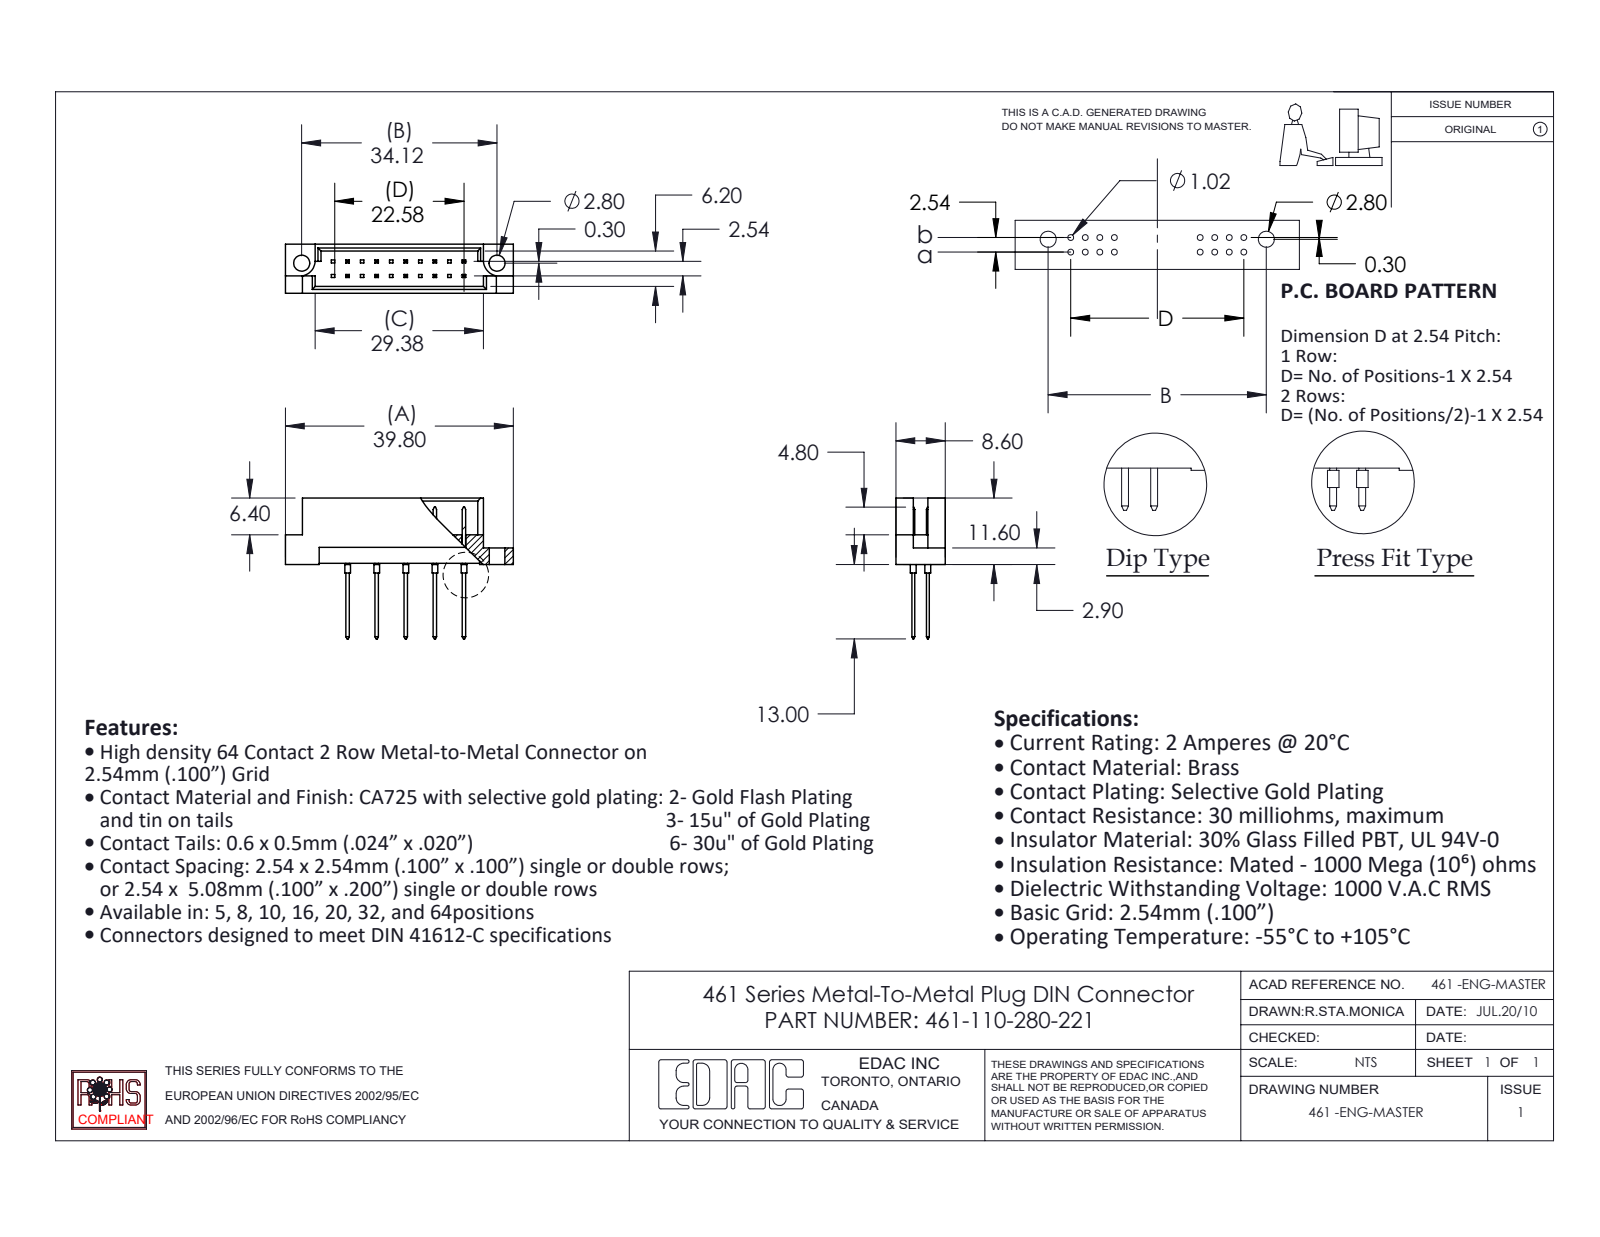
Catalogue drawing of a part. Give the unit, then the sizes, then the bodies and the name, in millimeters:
Units: millimetres
Overall size (bounding box): 39.8 × 24.6 × 8.6
Round holes (diameter × count): ⌀2.8 ×2
Round bosses / shafts (diameter × count): ⌀1 ×10
Partial cylindrical surfaces — rounded edges, fillets, slot ends (radius × count): R2.8 ×2
Main face-to-face distances: 1.2, 7.4, 8.6, 6.2, 5.08, 2.54, 2.78, 3.28, 5.32, 5.82
Hole centre spacings: 34.12
Volume: 1 980 mm³ · Surface area: 2 864 mm²
Bodies: 11 solids, 348 faces (322 planar, 26 cylindrical, 0 other)
Part name (STEP PRODUCT): 461 Part_20; 461-290_80; 461-110-280-221
STEP written by: SolidWorks 2020 (CONFIG_CONTROL_DESIGN)
